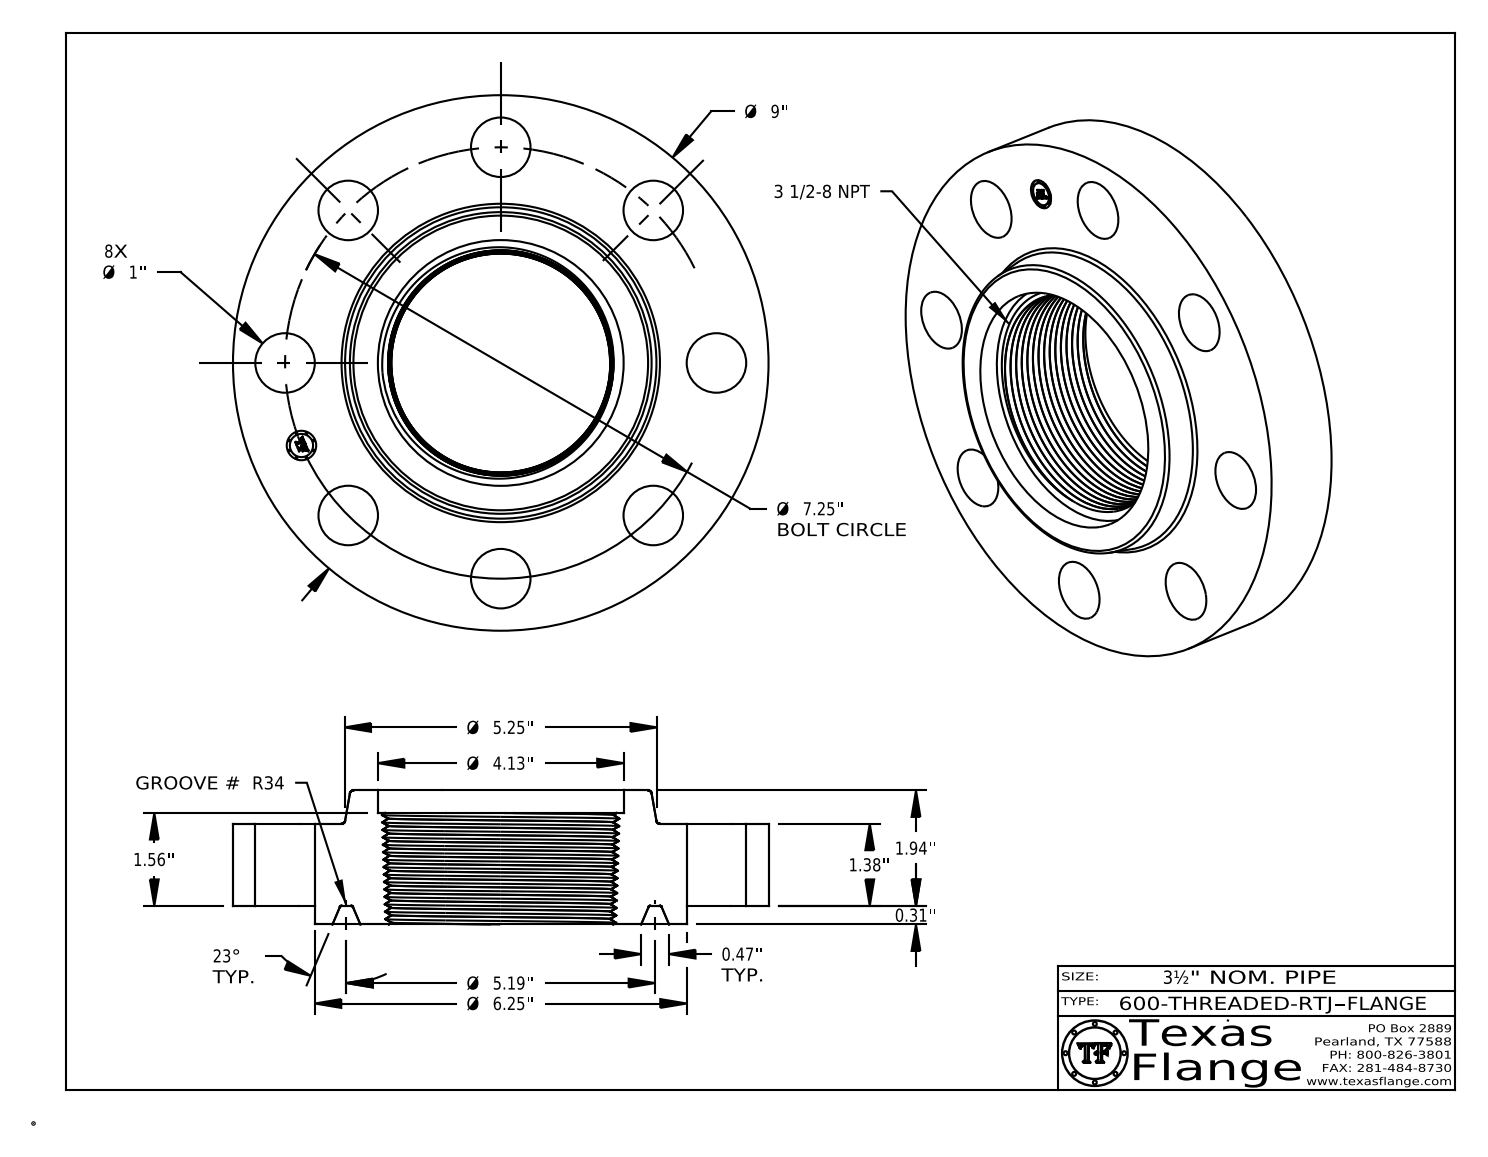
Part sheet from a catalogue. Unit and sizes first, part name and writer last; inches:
Units: inches
Overall size (bounding box): 9 × 9 × 2.253
Round holes (diameter × count): ⌀1 ×8, ⌀0.495 ×1, ⌀4.13 ×1
Round bosses / shafts (diameter × count): ⌀0.03 ×8, ⌀9 ×1, ⌀6.25 ×1, ⌀0.39 ×1
Main face-to-face distances: 1.38, 0.313, 1.693, 2.253, 1.94, 0.56, 1.872, 1.56, 0.18, 0.38
Hole centre spacings: 3.625, 2.774, 5.127, 6.698, 7.25, 1.415, 7.111, 4.028
Volume: 72 in³ · Surface area: 232.4 in²
Bodies: 1 solid, 584 faces (372 planar, 42 cylindrical, 170 other)
Part name (STEP PRODUCT): 600-THREADED-RTJ
STEP written by: CATIA V5 STEP AP214 (AUTOMOTIVE_DESIGN)
